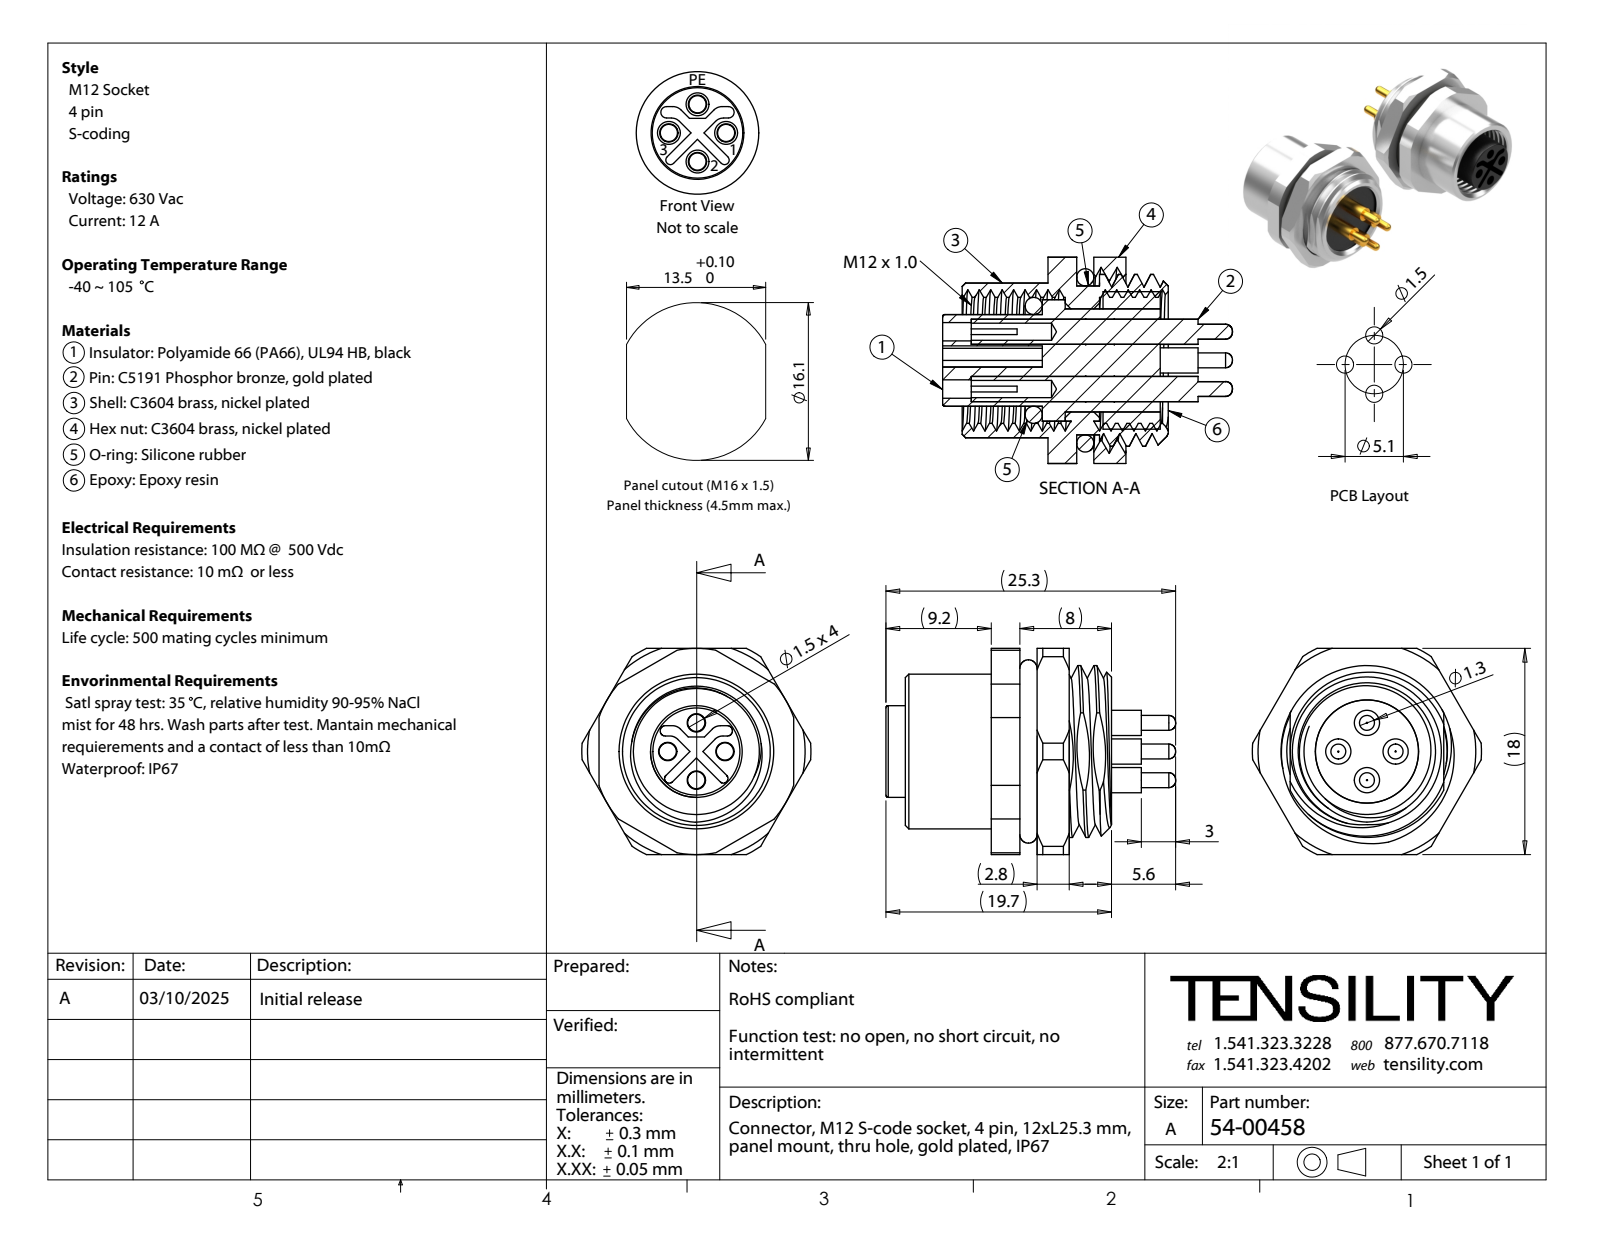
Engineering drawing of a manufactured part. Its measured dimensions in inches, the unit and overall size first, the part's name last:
Units: inches
Overall size (bounding box): 0.996 × 0.787 × 0.709
Round holes (diameter × count): ⌀0.059 ×4, ⌀0.063 ×4, ⌀0.354 ×1, ⌀0.433 ×1, ⌀0.551 ×1
Round bosses / shafts (diameter × count): ⌀0.087 ×4, ⌀0.051 ×4, ⌀0.531 ×1, ⌀0.512 ×1, ⌀0.472 ×1, ⌀0.417 ×1, ⌀0.315 ×1
Partial cylindrical surfaces — rounded edges, fillets, slot ends (radius × count): R0.039 ×4, R0.016 ×2, R0.018 ×2, R0.295 ×1, R0.354 ×1, R0.394 ×1
Main face-to-face distances: 0.118, 0.098, 0.287, 0.031, 0.209, 0.079, 0.059, 0.02, 0.197, 0.386
Hole centre spacings: 0.098, 0.139, 0.197
Volume: 0.169 in³ · Surface area: 9.312 in²
Bodies: 10 solids, 330 faces (105 planar, 141 cylindrical, 84 other)
Part name (STEP PRODUCT): 54-00458-02; 54-00458-04; 54-00458-06; 54-00458-05 (+3 more)
STEP written by: SolidWorks 2021 (CONFIG_CONTROL_DESIGN)
